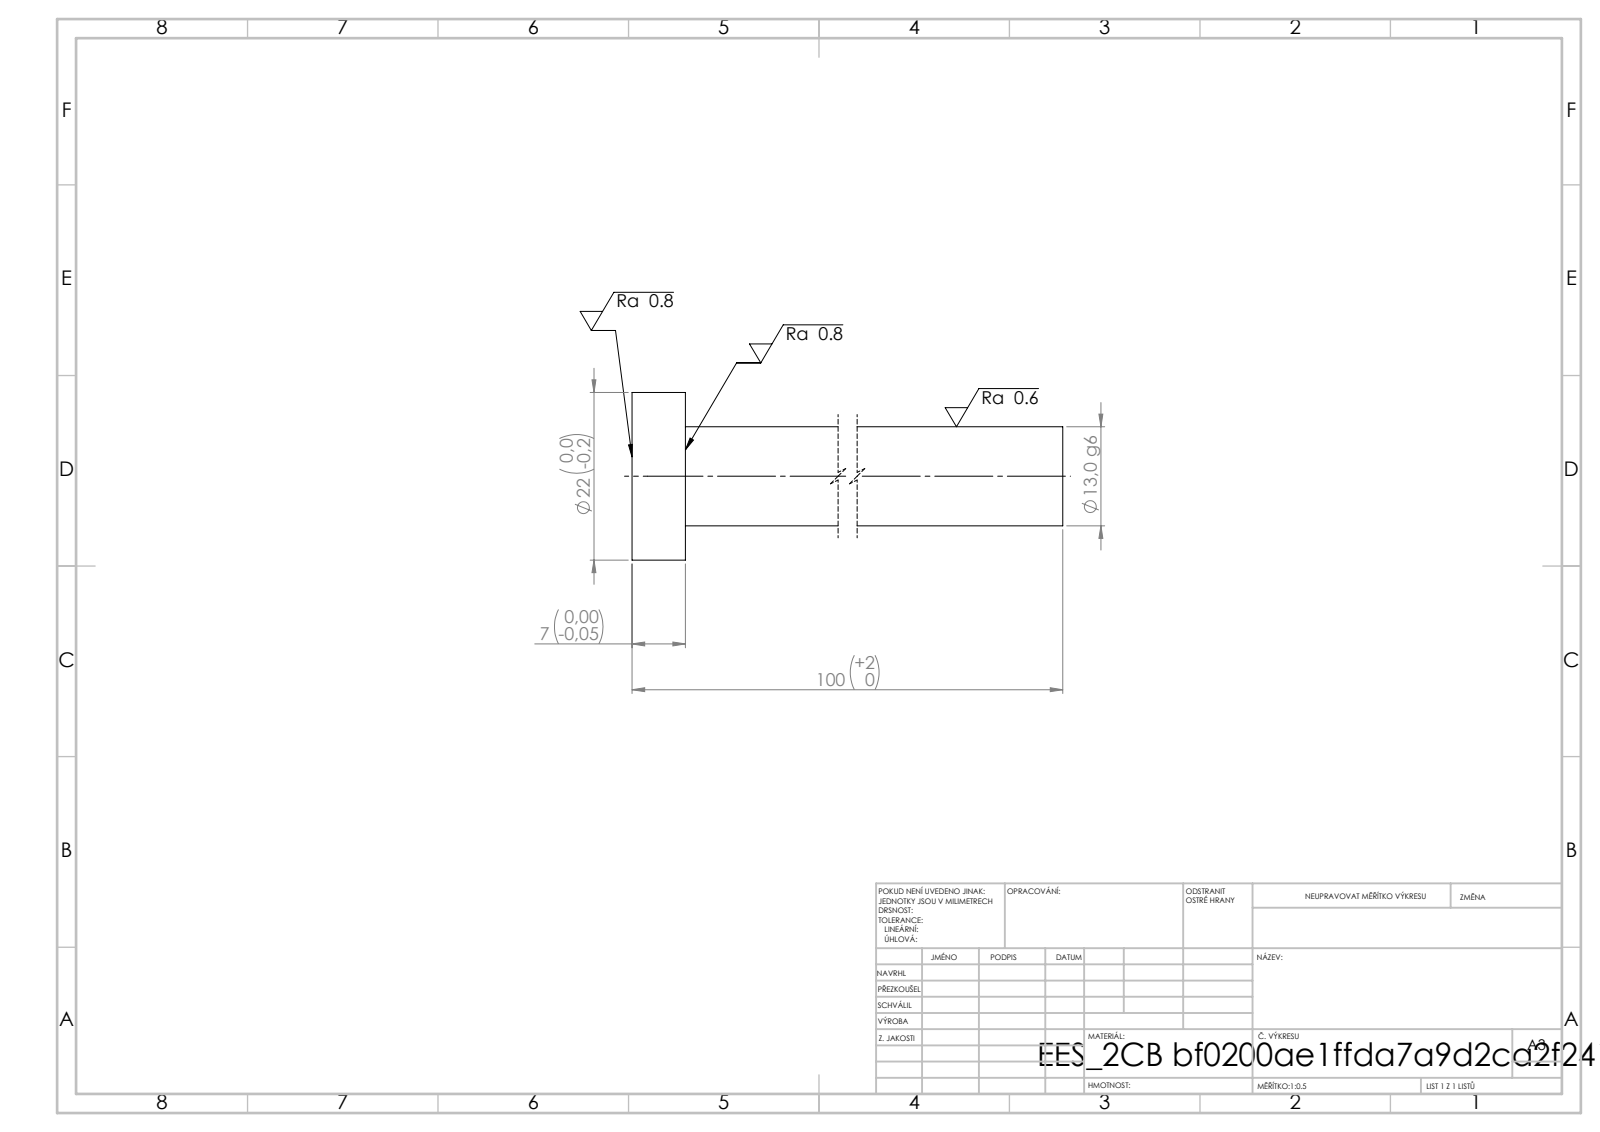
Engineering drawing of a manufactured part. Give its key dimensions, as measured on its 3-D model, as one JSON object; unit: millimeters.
{"step_written_by": "SolidWorks 2019 (CONFIG_CONTROL_DESIGN)", "units": "millimeters", "bodies": {"solids": 1, "faces": 7, "planar": 3, "cylindrical": 4, "other": 0}, "overall_size": [100, 22, 22], "volume_mm3": 15005, "surface_area_mm2": 5042, "round_bosses_or_shafts": [[22, 1], [13, 1]], "face_to_face_distances": [7, 100, 93]}
